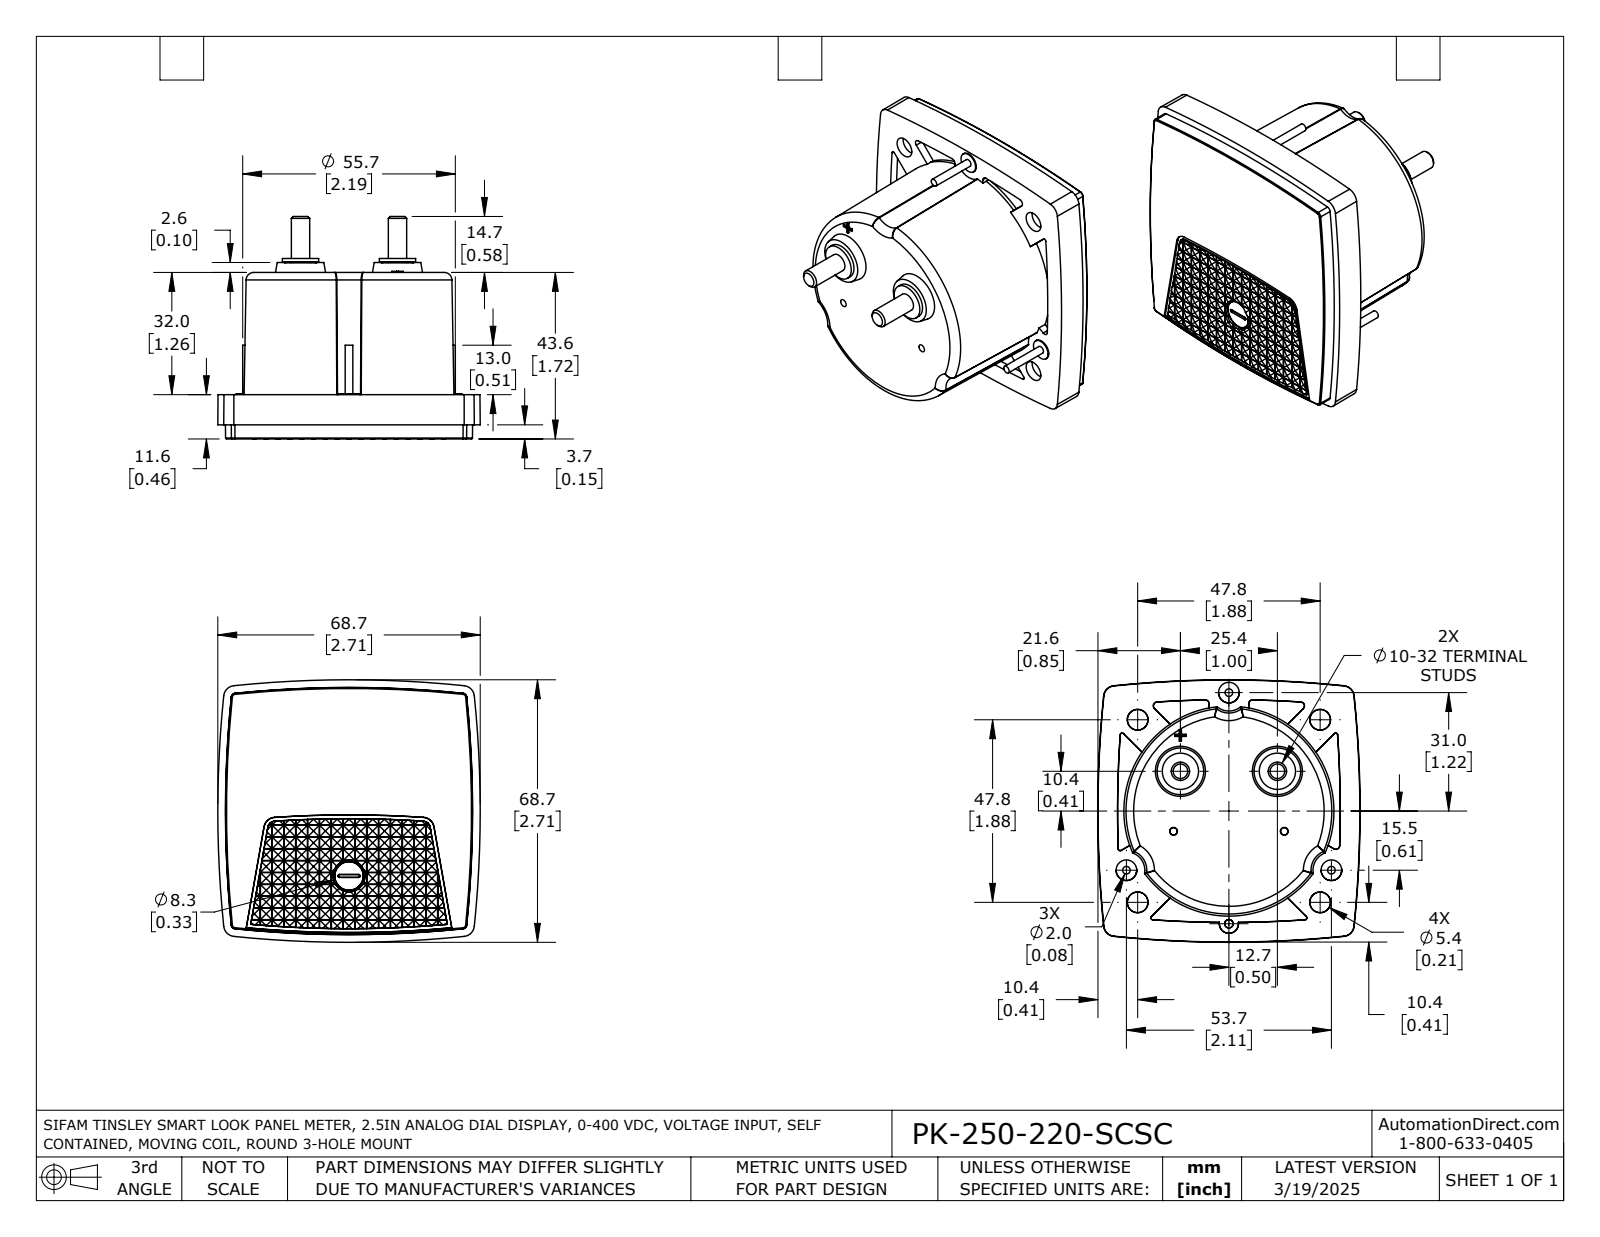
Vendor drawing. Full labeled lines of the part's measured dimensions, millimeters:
Part name (STEP PRODUCT): PK-250-220-SCSC
STEP written by: SolidWorks 2021 (AUTOMOTIVE_DESIGN)
Units: millimetres
Bodies: 1 solid, 1550 faces (1165 planar, 265 cylindrical, 120 other)
Overall size (bounding box): 68.7 × 68.7 × 58.3
Volume: 124 400 mm³ · Surface area: 19 620 mm²
Round bosses / shafts (diameter × count): ⌀5.4 ×3, ⌀2 ×3, ⌀9.5 ×2, ⌀4.8 ×2, ⌀5.5 ×1
Partial cylindrical surfaces — rounded edges, fillets, slot ends (radius × count): R4.2 ×2, R27.5 ×1
Main face-to-face distances: 43.6, 32, 11.6, 0.6, 2.2, 2.4, 7.9, 3, 1.8, 34.2
